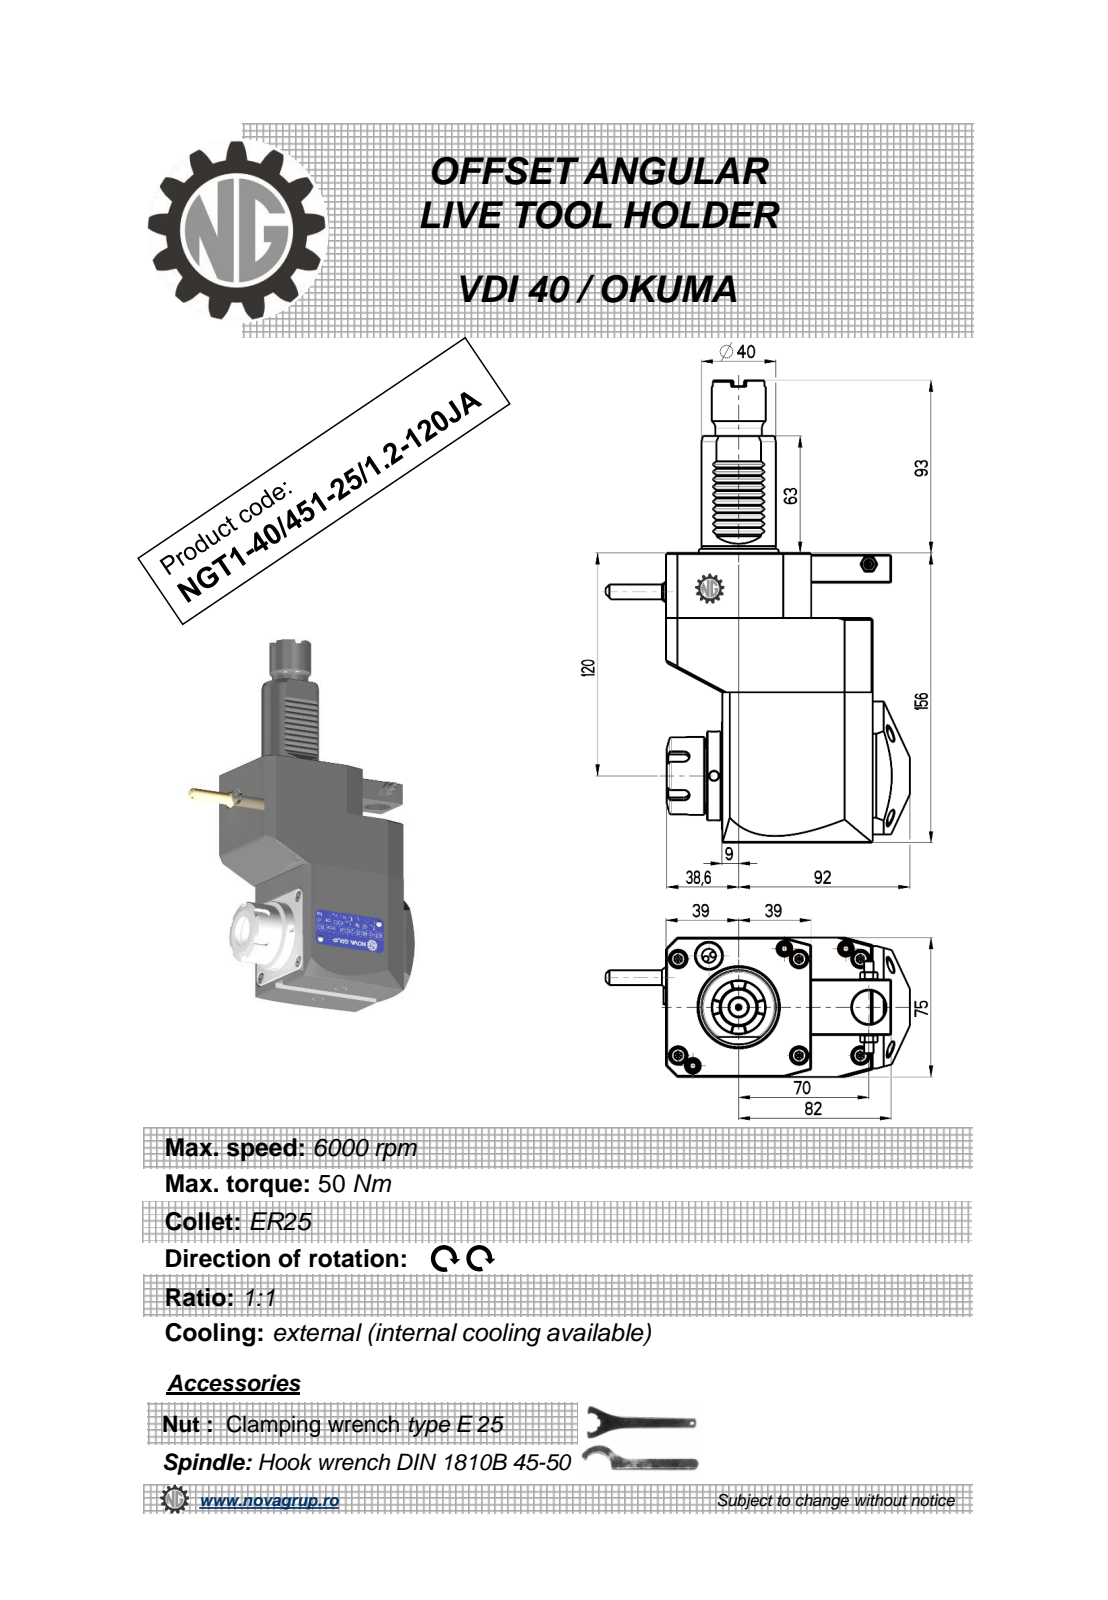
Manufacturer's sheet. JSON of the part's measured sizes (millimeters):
{"part_name": "NGT1_40_451_25_1_2_120JA", "step_written_by": "PRO/ENGINEER BY PARAMETRIC TECHNOLOGY CORPORATION, 2010280 (CONFIG_CONTROL_DESIGN)", "units": "millimeters", "bodies": {"solids": 1, "faces": 502, "planar": 218, "cylindrical": 97, "other": 187}, "overall_size": [249, 163.5, 76.6], "volume_mm3": 1197000, "surface_area_mm2": 91253, "round_holes": [[5, 3], [3, 1], [4.2, 1], [9.5, 1], [18, 1], [20.3, 1], [26.8, 1]], "round_bosses_or_shafts": [[48, 1], [42, 1], [40, 1], [37.5, 1], [33, 1], [29, 1], [26.58, 1], [25, 1]], "partial_cylinders_radius": [[0.26, 12], [0.3, 10], [0.2, 6], [3, 5], [0.5, 1], [10, 1], [40, 1]], "face_to_face_distances": [75, 156, 111, 30, 121, 35, 81, 48, 33, 78], "hole_center_spacings": [13.25, 20.93, 70, 83.25, 100.28, 112.5, 141.16]}
